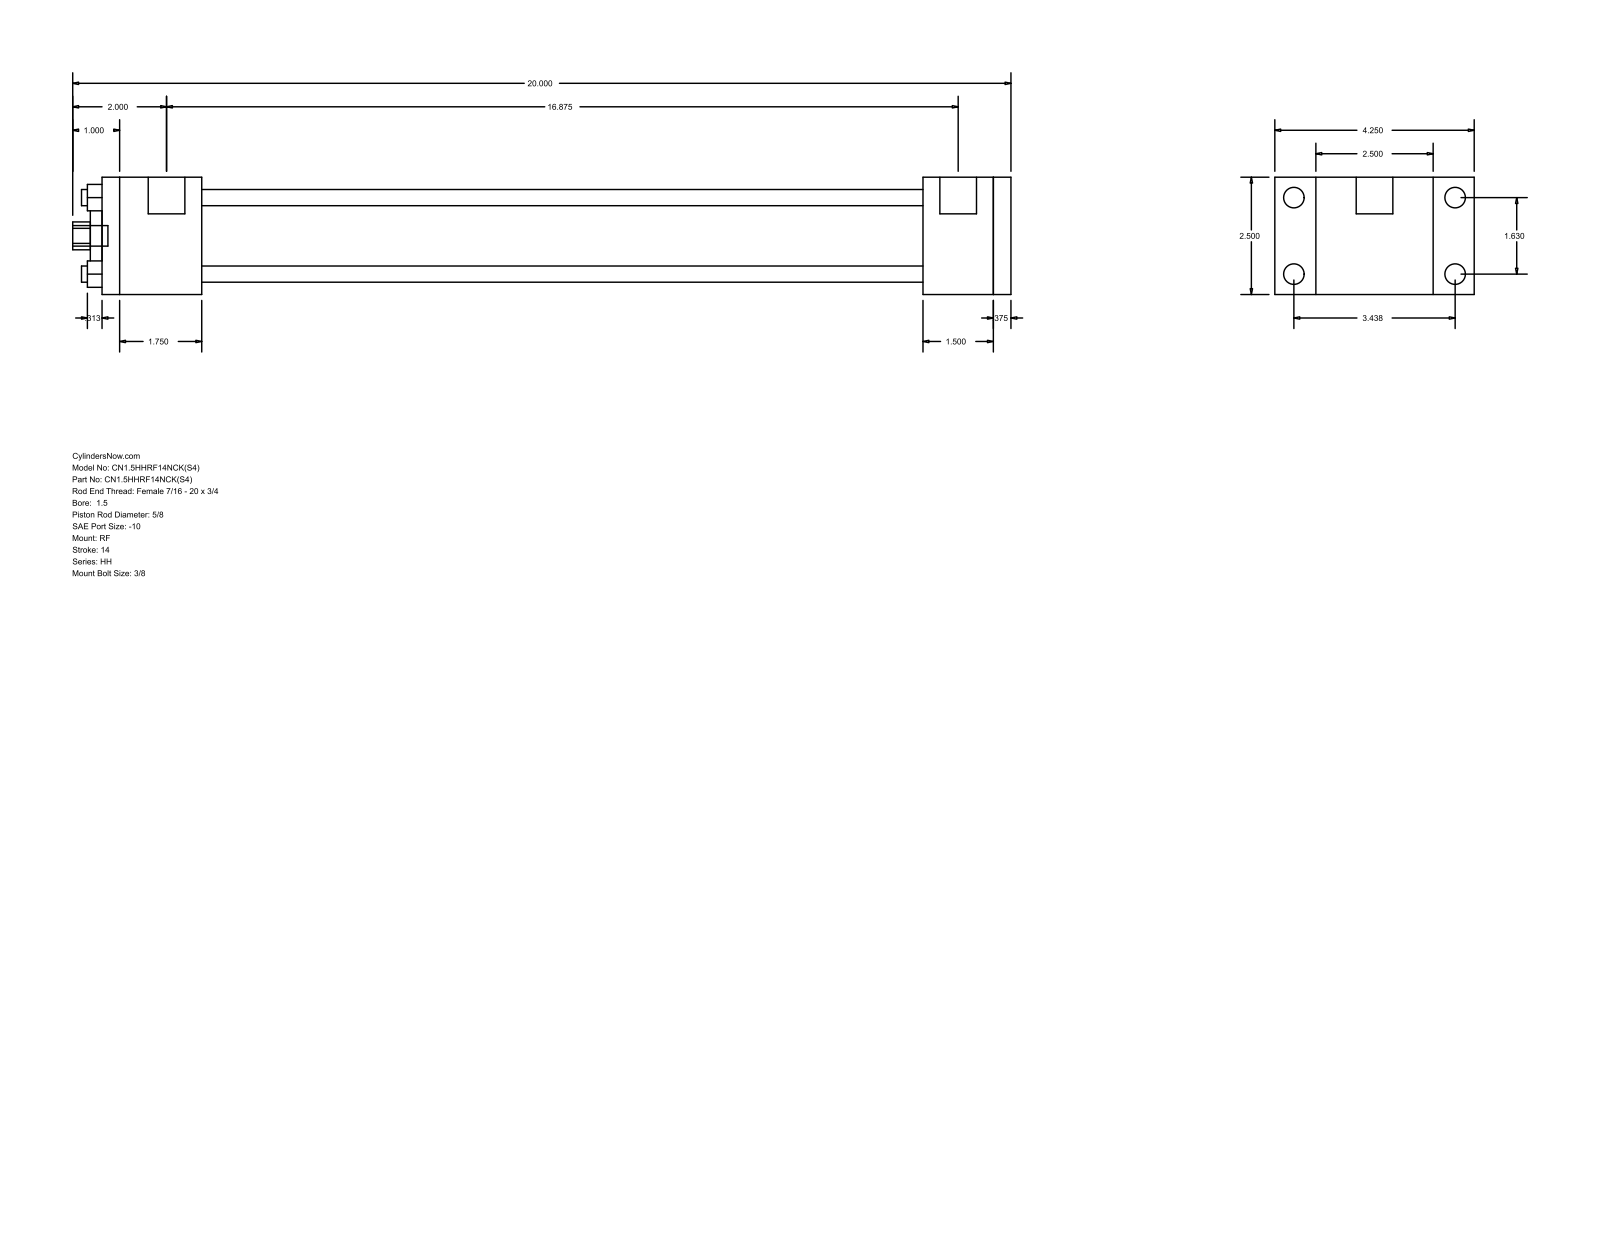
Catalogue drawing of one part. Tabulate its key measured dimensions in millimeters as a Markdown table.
| quantity | value |
| --- | --- |
| part name | HH_RF__0150_0.625 |
| STEP written by | GSSL Pune (CONFIG_CONTROL_DESIGN) |
| units | millimeters |
| bodies | 0 solids, 92 faces (64 planar, 28 cylindrical, 0 other) |
| overall size | 508 × 107.95 × 63.5 |
| round holes (diameter × count) | 8.76 × 4, 15.88 × 1, 28.57 × 1, 44.45 × 1 |
| round bosses / shafts (diameter × count) | 11.13 × 4, 5.56 × 4, 19.84 × 2, 11.11 × 1 |
| partial cylindrical surfaces (radius × count) | 7.54 × 1 |
| main face-to-face distances | 63.5, 492.12, 9.52, 38.1, 482.6, 53.97, 444.5, 390.53, 428.63, 438.15 |
| hole center spacings | 29.27, 41.4, 58.55 |
